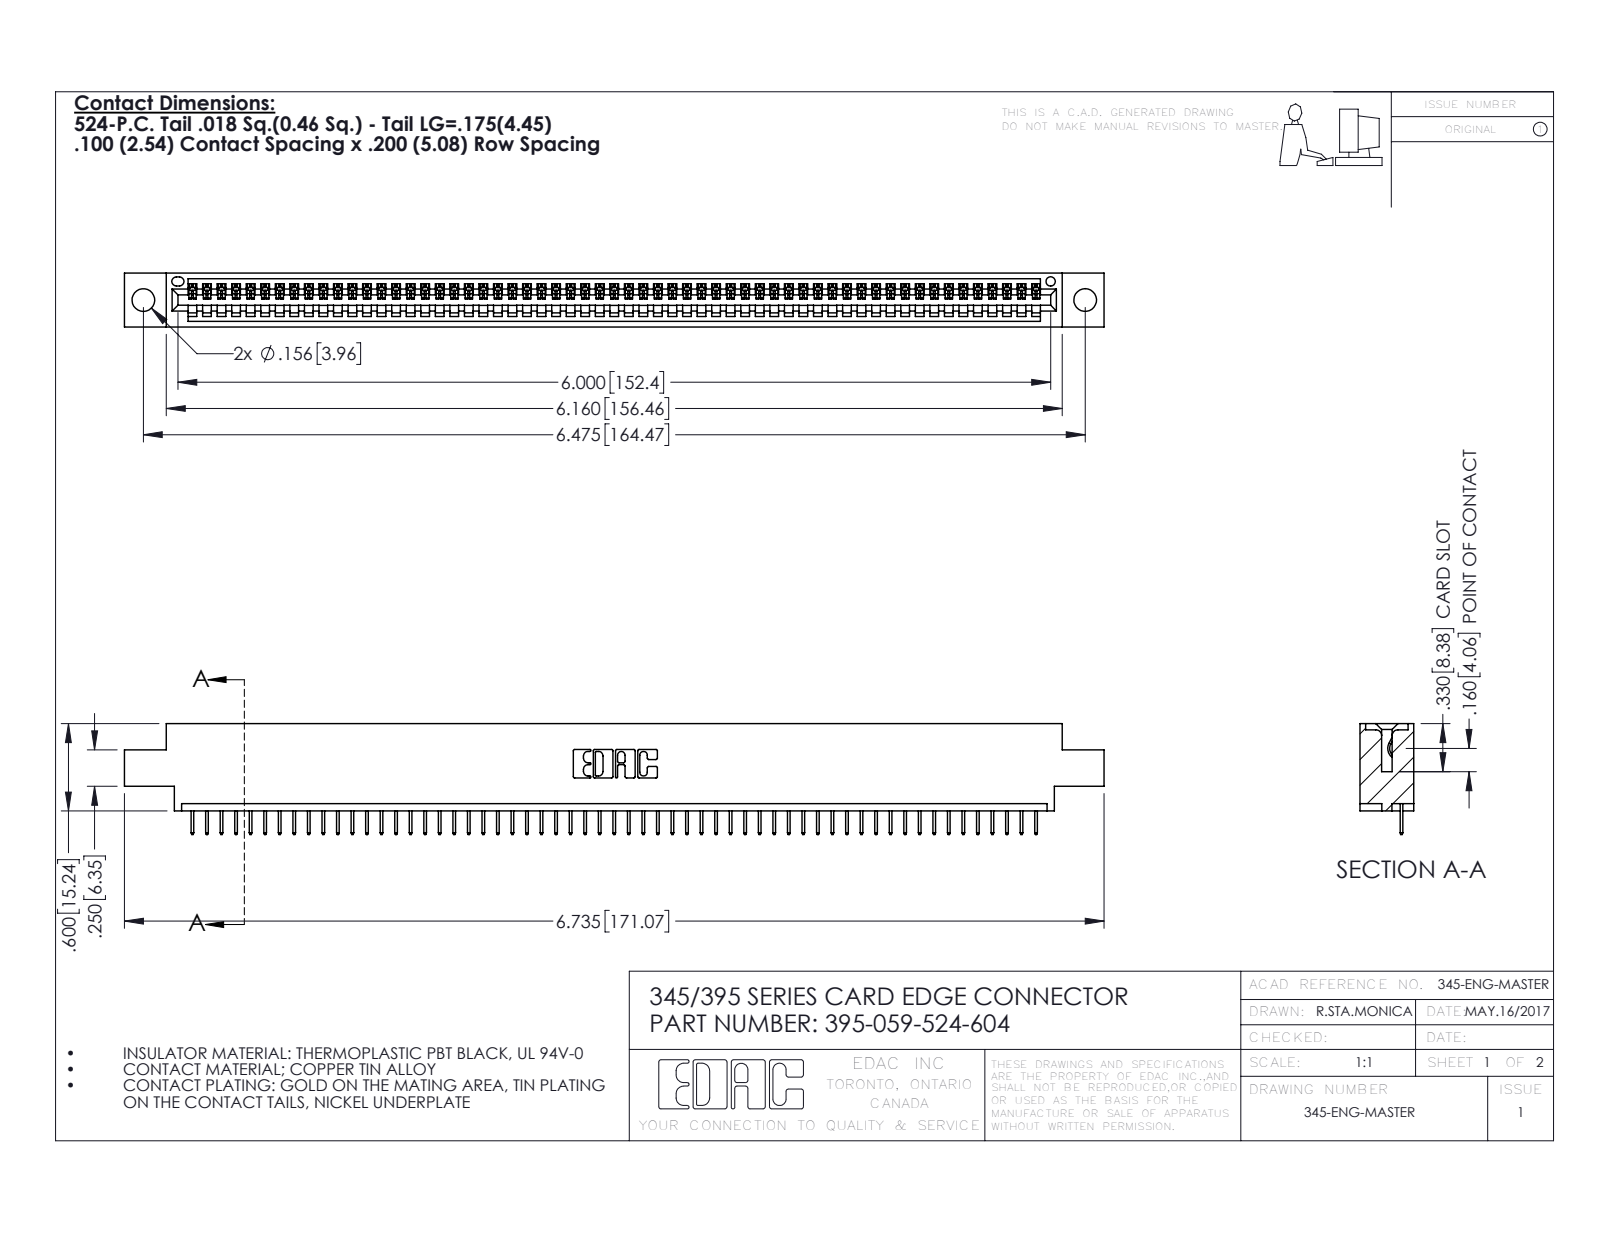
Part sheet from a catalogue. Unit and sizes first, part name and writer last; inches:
Units: inches
Overall size (bounding box): 6.735 × 0.762 × 0.37
Round holes (diameter × count): ⌀0.156 ×2, ⌀0.064 ×1
Partial cylindrical surfaces — rounded edges, fillets, slot ends (radius × count): R0.006 ×118, R0.01 ×22, R0.007 ×6, R0.031 ×6, R0.026 ×3, R0.031 ×2, R0.04 ×2, R0.014 ×1
Main face-to-face distances: 0.072, 0.298, 0.37, 0.2, 0.098, 0.272, 0.025, 0.225, 0.072, 0.175
Hole centre spacings: 0.27, 6.239, 6.475
Volume: 0.974 in³ · Surface area: 31.96 in²
Bodies: 60 solids, 3788 faces (2798 planar, 990 cylindrical, 0 other)
Part name (STEP PRODUCT): 345 Part_0.170 Offset - 0.156 Dia-TH; 345-292-001_345-293-124; 395-059-524-604
STEP written by: SolidWorks 2016 (CONFIG_CONTROL_DESIGN)
